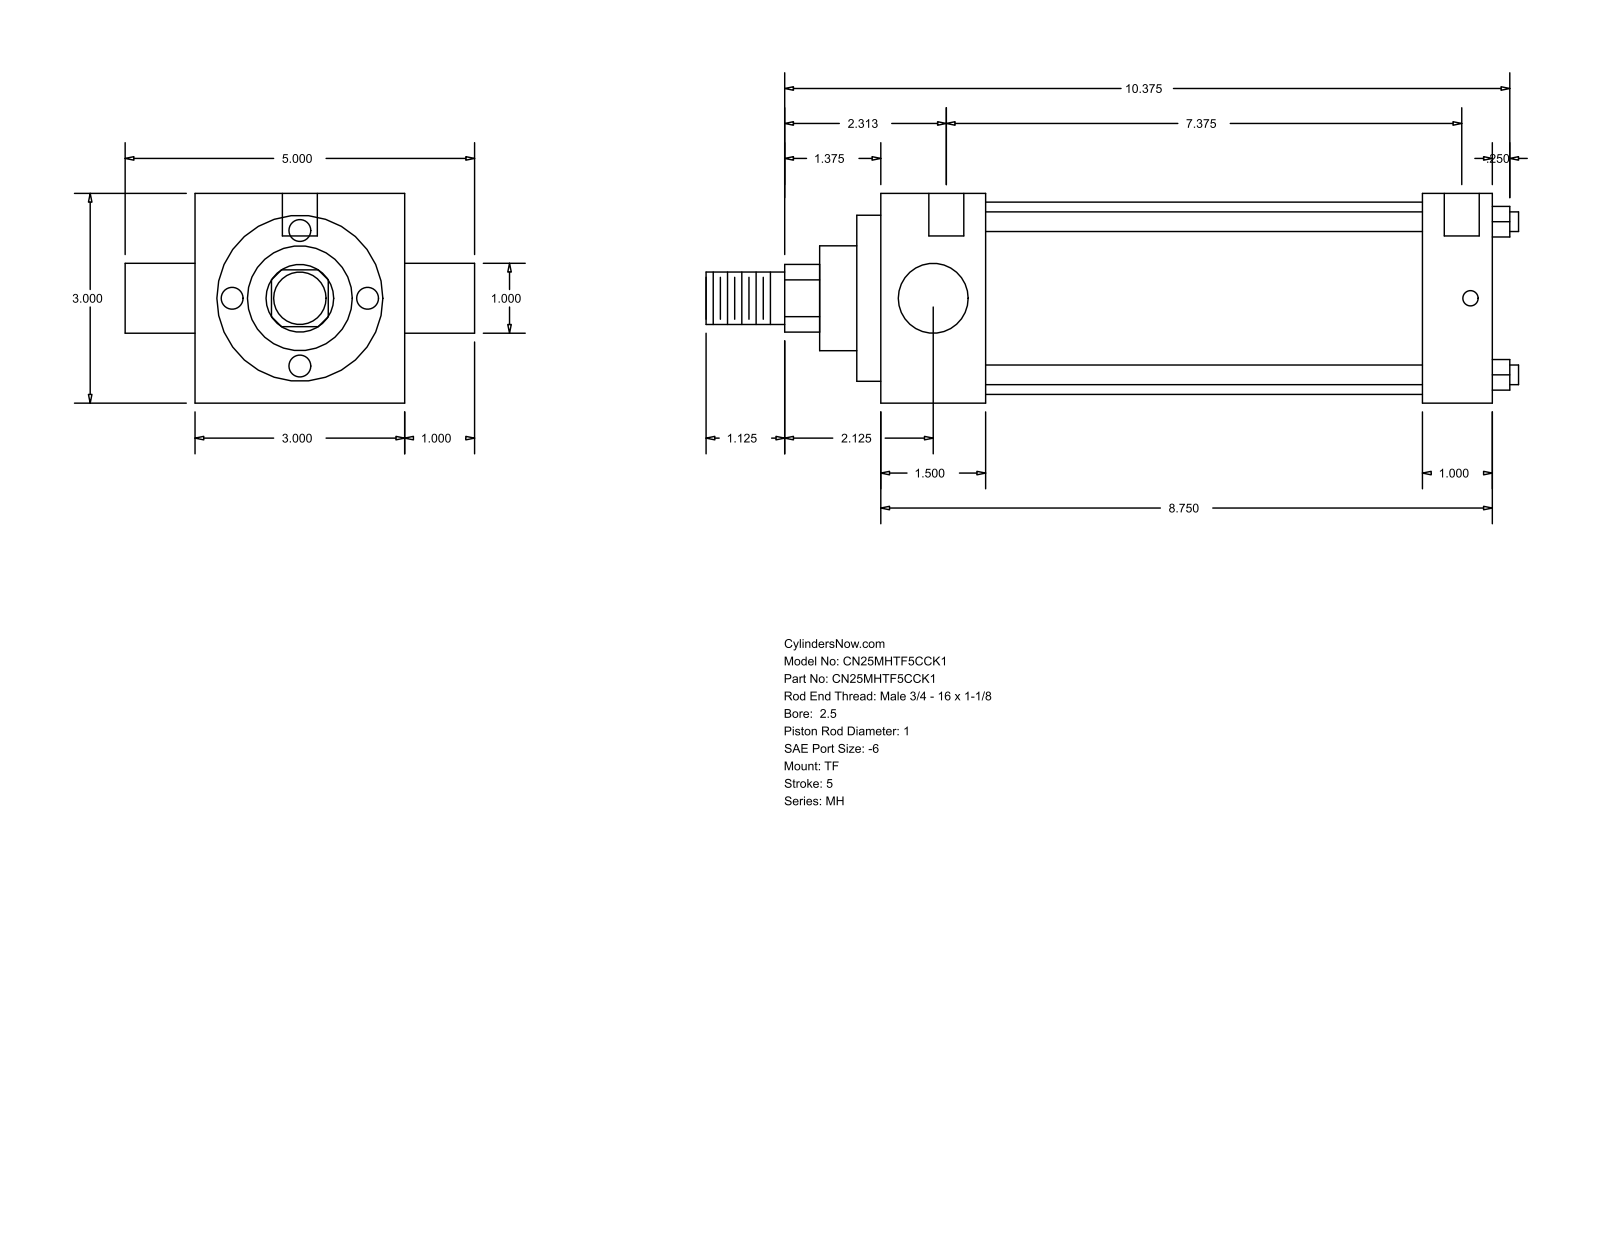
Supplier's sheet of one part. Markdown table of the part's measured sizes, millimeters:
| quantity | value |
| --- | --- |
| part name | MH_TF__0250_1 |
| STEP written by | GSSL Pune (CONFIG_CONTROL_DESIGN) |
| units | millimeters |
| bodies | 0 solids, 86 faces (61 planar, 25 cylindrical, 0 other) |
| overall size | 295.27 × 127 × 76.2 |
| round holes (diameter × count) | 5.56 × 3, 12.7 × 2 |
| round bosses / shafts (diameter × count) | 7.14 × 4, 25.4 × 2, 69.85 × 1, 60.33 × 1, 38.1 × 1, 19.05 × 1 |
| partial cylindrical surfaces (radius × count) | 12.29 × 1 |
| main face-to-face distances | 76.2, 222.26, 25.4, 38.11, 184.15, 196.86, 158.75, 8.73, 46.84, 205.59 |
| hole center spacings | 3.18, 4.76, 187.32, 190.5, 192.08, 195.26 |
